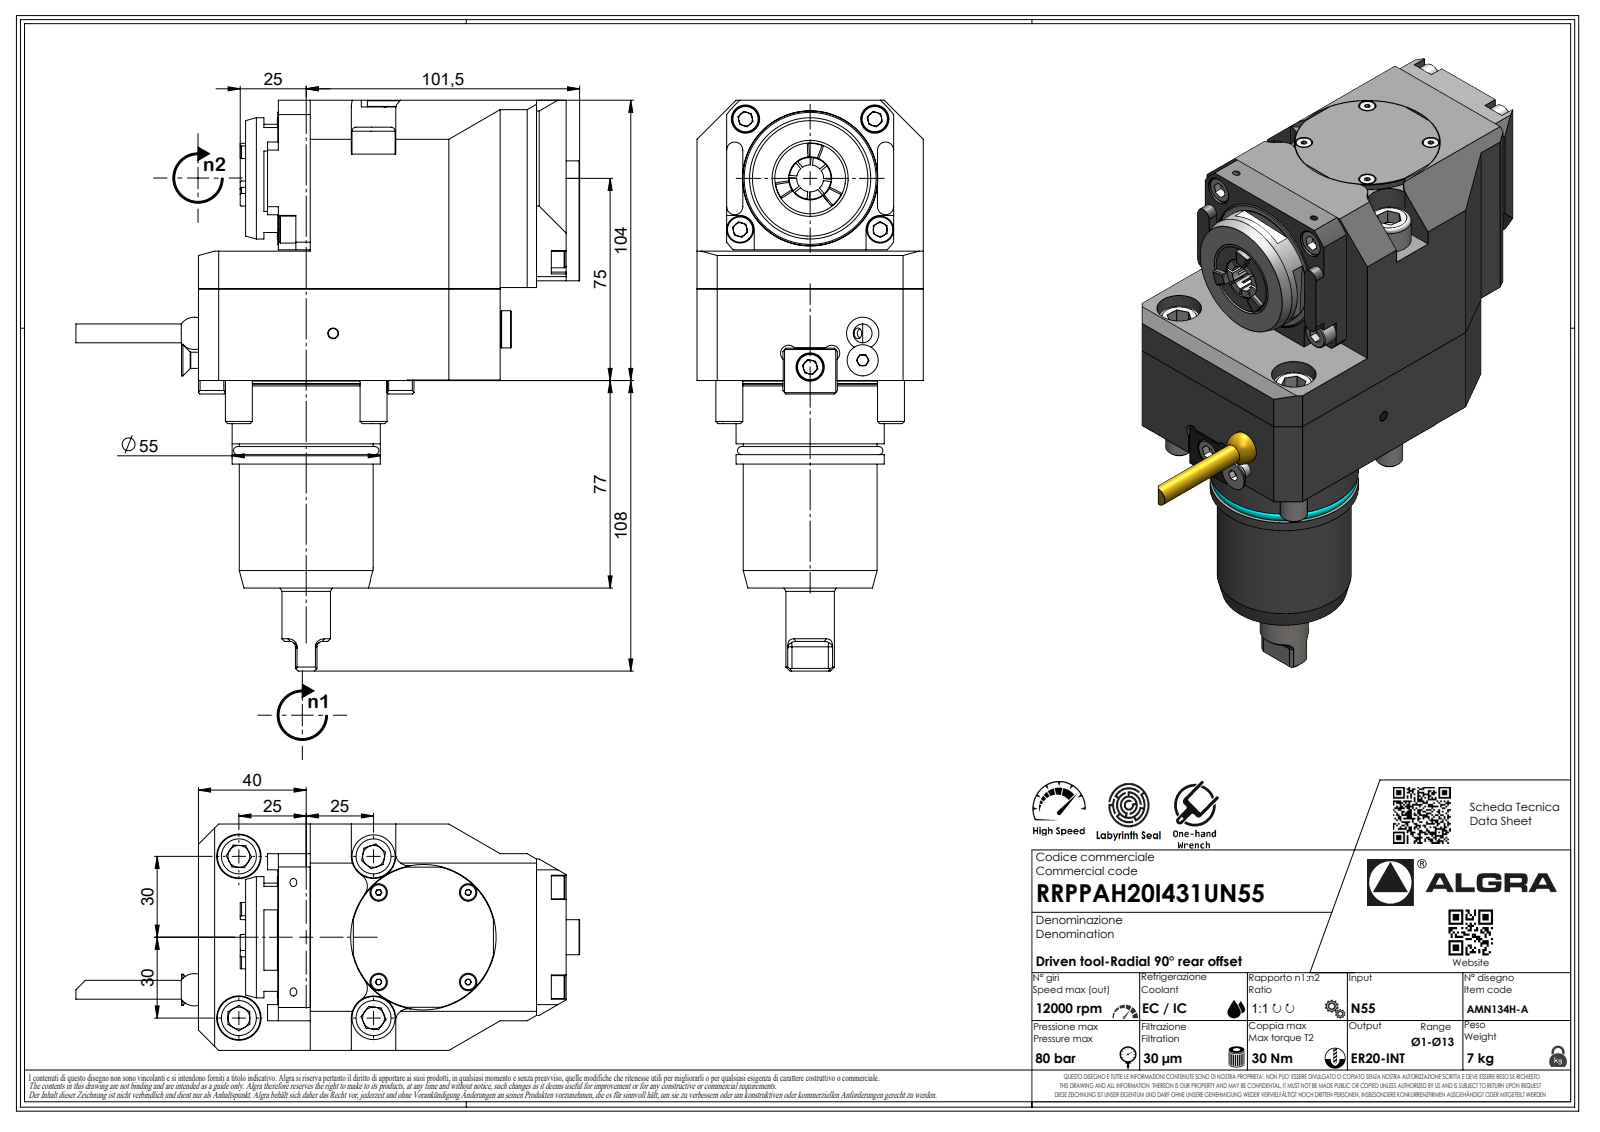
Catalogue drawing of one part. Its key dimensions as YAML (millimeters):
part_name: "RRPPAH20I431UN55"
step_written_by: "SolidWorks 2023 (AUTOMOTIVE_DESIGN)"
units: millimeters
bodies: {solids: 1, faces: 599, planar: 399, cylindrical: 85, other: 115}
overall_size: [211.8, 187, 84]
volume: 1070000
surface_area: 84883
round_holes:
  - {diameter: 16.5, count: 2}
  - {diameter: 2.1, count: 1}
  - {diameter: 4, count: 1}
  - {diameter: 54, count: 1}
round_bosses_or_shafts:
  - {diameter: 16, count: 4}
  - {diameter: 10, count: 4}
  - {diameter: 55, count: 1}
  - {diameter: 54.6, count: 1}
  - {diameter: 49.7, count: 1}
  - {diameter: 45, count: 1}
  - {diameter: 18, count: 1}
  - {diameter: 7, count: 1}
partial_cylinders:
  - {radius: 0.33, count: 7}
  - {radius: 0.52, count: 7}
  - {radius: 2, count: 7}
  - {radius: 3.7, count: 7}
  - {radius: 3, count: 4}
  - {radius: 5, count: 4}
  - {radius: 8.25, count: 3}
  - {radius: 0.21, count: 1}
face_to_face_distances: [84, 104, 11, 73, 56, 24.5, 48, 112, 136.5, 62]
hole_center_spacings: [74.78, 60]
